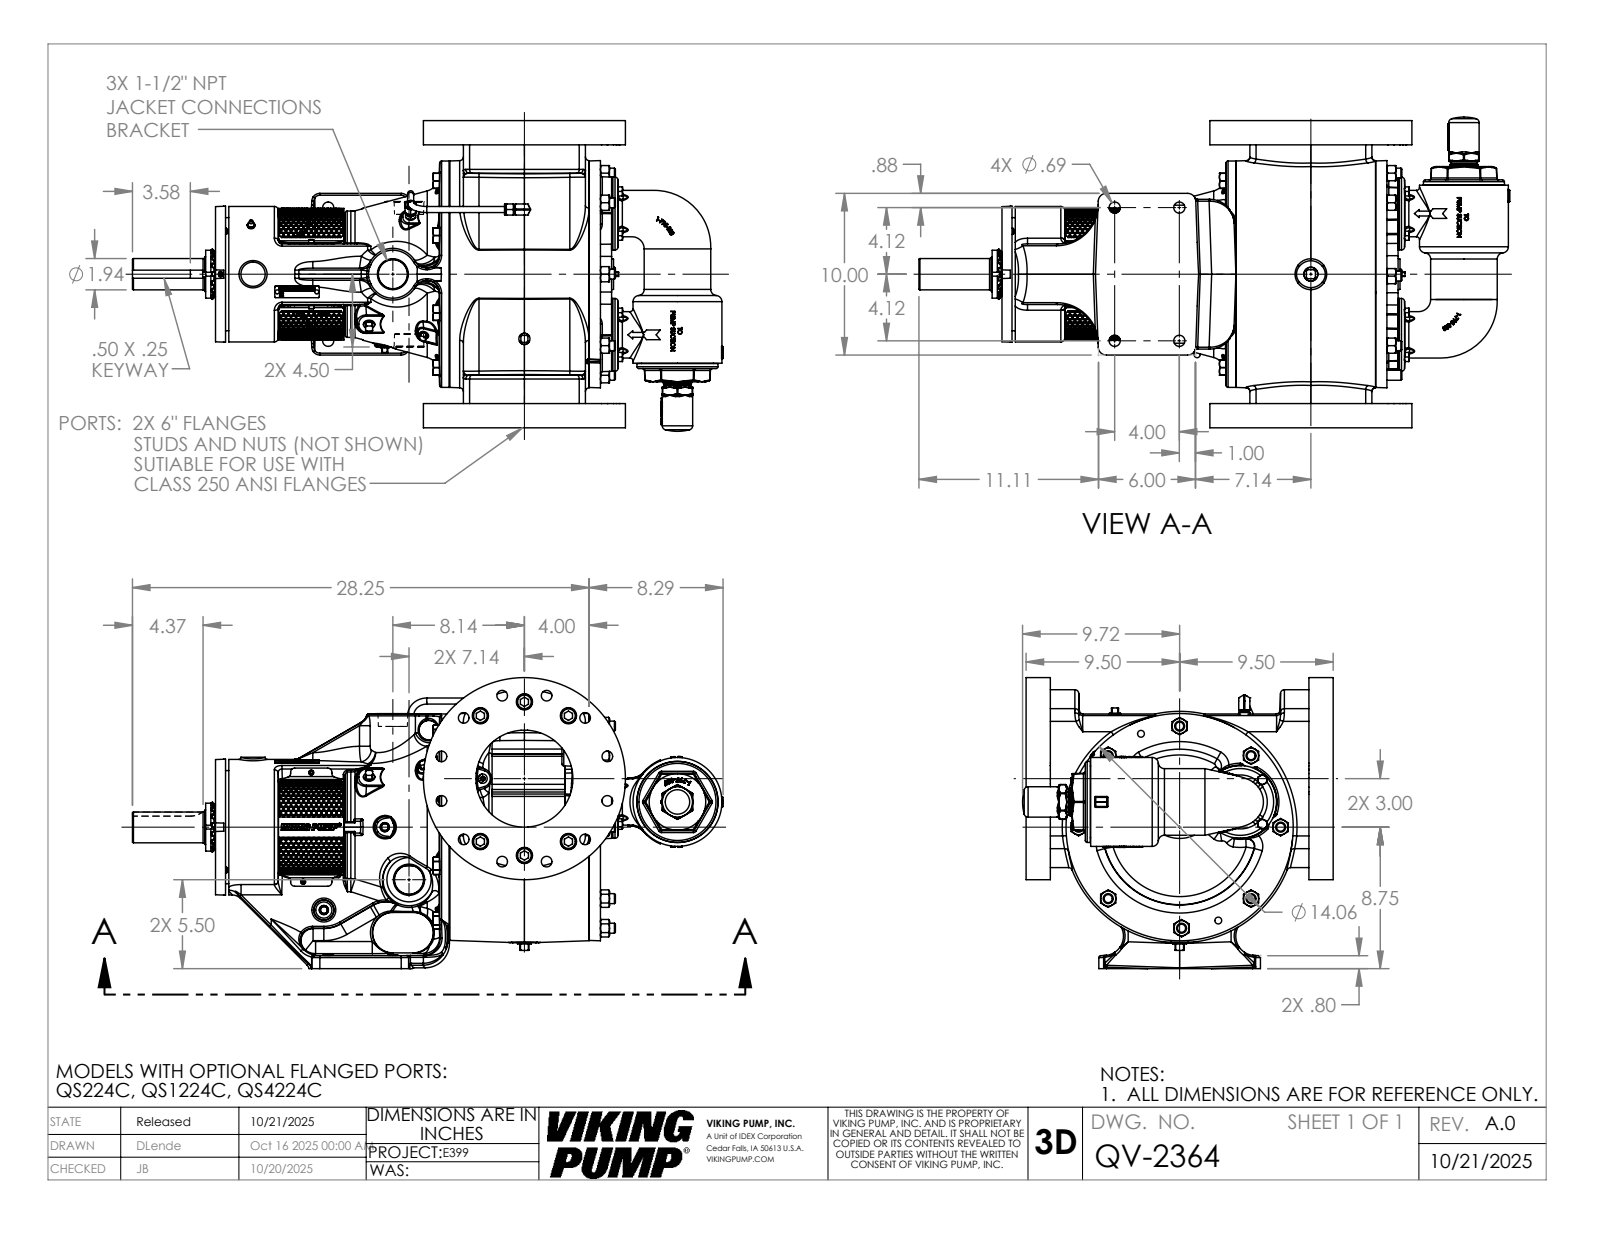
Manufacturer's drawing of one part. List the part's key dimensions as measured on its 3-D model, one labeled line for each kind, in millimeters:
Part name (STEP PRODUCT): QV-2364
STEP written by: SolidWorks 2024 (AUTOMOTIVE_DESIGN)
Units: millimetres
Bodies: 1 solid, 4894 faces (1620 planar, 770 cylindrical, 2504 other)
Overall size (bounding box): 928.2 × 488.2 × 457.2
Volume: 52 010 000 mm³ · Surface area: 1 807 000 mm²
Round holes (diameter × count): ⌀16.7 ×12, ⌀6.4 ×9, ⌀6.8 ×8, ⌀29.4 ×8, ⌀25.4 ×6, ⌀17.5 ×4, ⌀4 ×2, ⌀8 ×2, ⌀10.7 ×2, ⌀11.5 ×1, ⌀36.4 ×1, ⌀54.8 ×1
Round bosses / shafts (diameter × count): ⌀15.7 ×8, ⌀23.8 ×6, ⌀9.5 ×5, ⌀7.9 ×3, ⌀4.8 ×3, ⌀114.3 ×2, ⌀17.4 ×2, ⌀14.3 ×2
Partial cylindrical surfaces — rounded edges, fillets, slot ends (radius × count): R3 ×60, R19.1 ×22, R1.5 ×20, R0.4 ×18, R2.3 ×18, R1.8 ×16, R0.8 ×13, R12.7 ×12
Main face-to-face distances: 38.1, 444.5, 482.6, 406.4, 14.5, 605, 97, 507.9, 565.6, 202.5
Hole centre spacings: 135, 95.3, 52.8, 260.7, 146.9, 68.9, 69.9, 79.6
